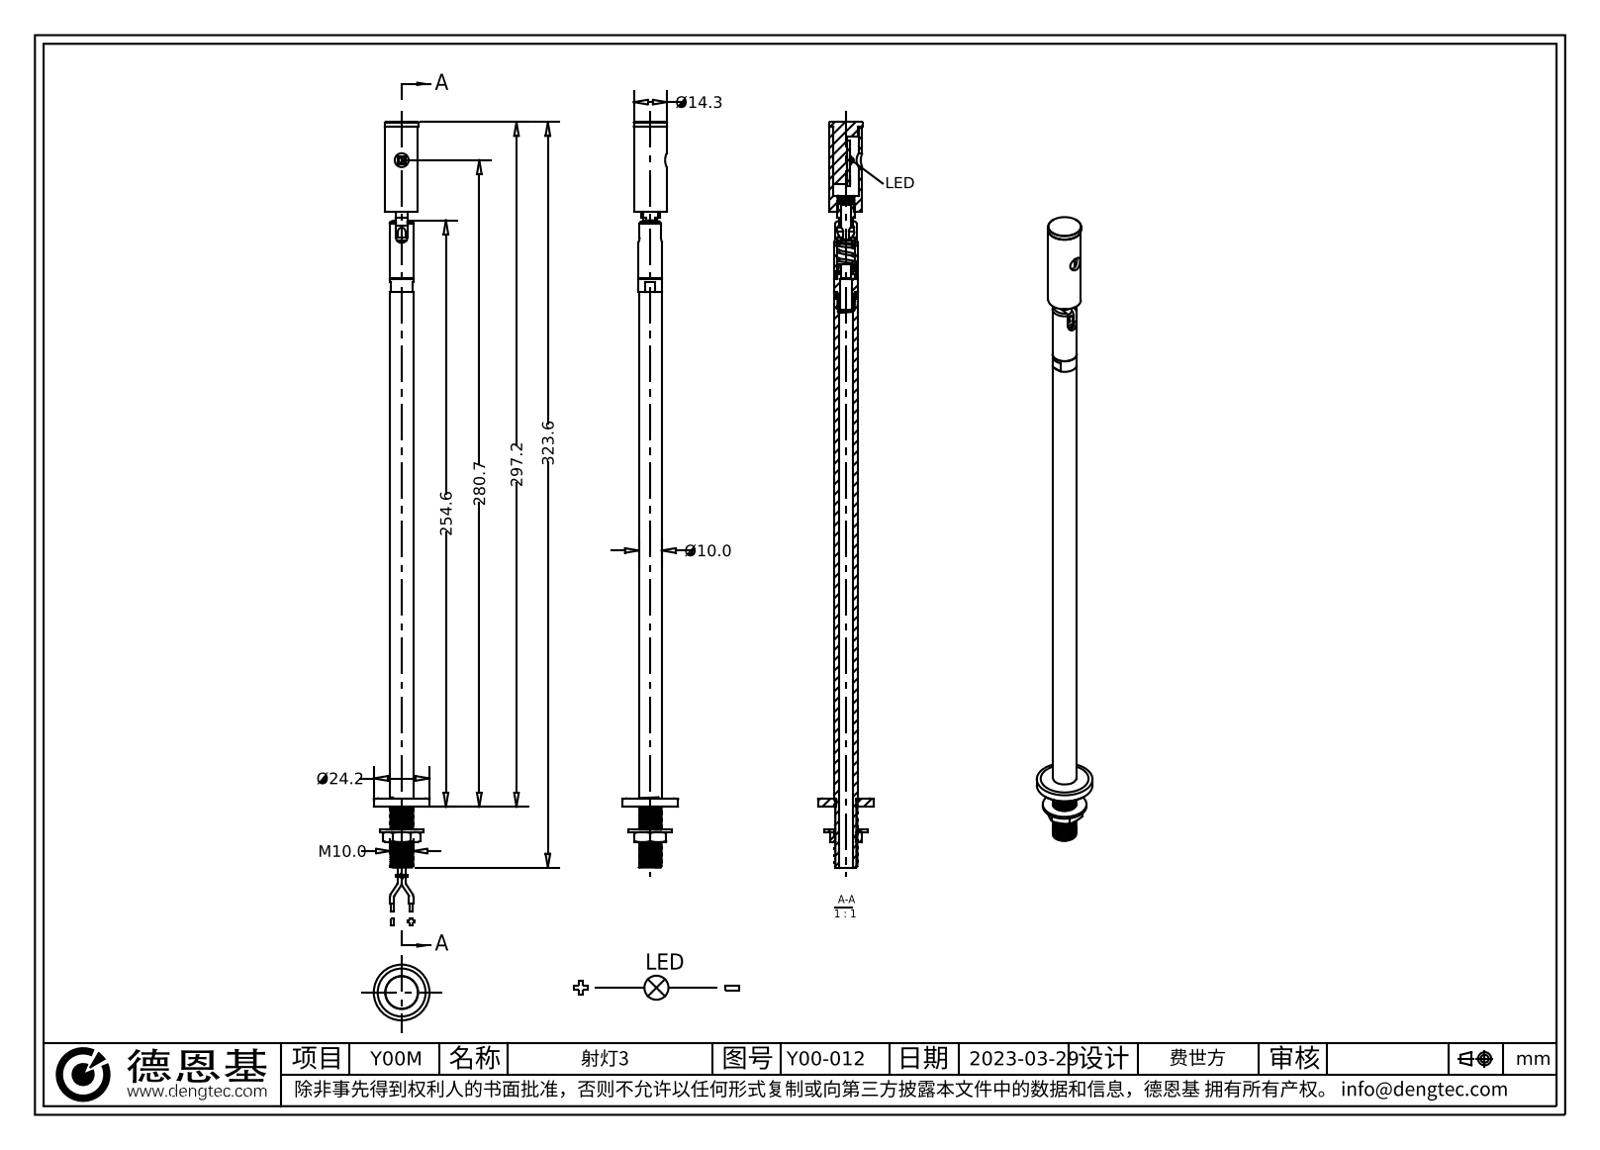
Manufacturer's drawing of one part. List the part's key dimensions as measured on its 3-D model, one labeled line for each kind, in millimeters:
Part name (STEP PRODUCT): 灯板1; 六角螺母M10; 底座压板; 弹簧 (+8 more)
STEP written by: SolidWorks 2018 (CONFIG_CONTROL_DESIGN)
Units: millimetres
Bodies: 19 solids, 355 faces (114 planar, 177 cylindrical, 64 other)
Overall size (bounding box): 323.6 × 24.2 × 24.2
Volume: 21 164 mm³ · Surface area: 24 027 mm²
Round holes (diameter × count): ⌀4 ×1, ⌀4.5 ×1, ⌀5.4 ×1, ⌀5.8 ×1, ⌀6 ×1, ⌀6.8 ×1, ⌀8.5 ×1, ⌀9.2 ×1, ⌀10.2 ×1, ⌀11 ×1
Round bosses / shafts (diameter × count): ⌀24.2 ×1, ⌀19 ×1, ⌀14.3 ×1, ⌀14.2 ×1, ⌀10.7 ×1, ⌀10.5 ×1, ⌀10 ×1, ⌀8 ×1
Partial cylindrical surfaces — rounded edges, fillets, slot ends (radius × count): R0.2 ×4, R0.5 ×4, R1.6 ×1, R2.5 ×1, R3.1 ×1, R4.2 ×1
Main face-to-face distances: 11, 3.6, 14.6, 1, 10, 13.6, 1.19, 291.6, 39, 308.2
